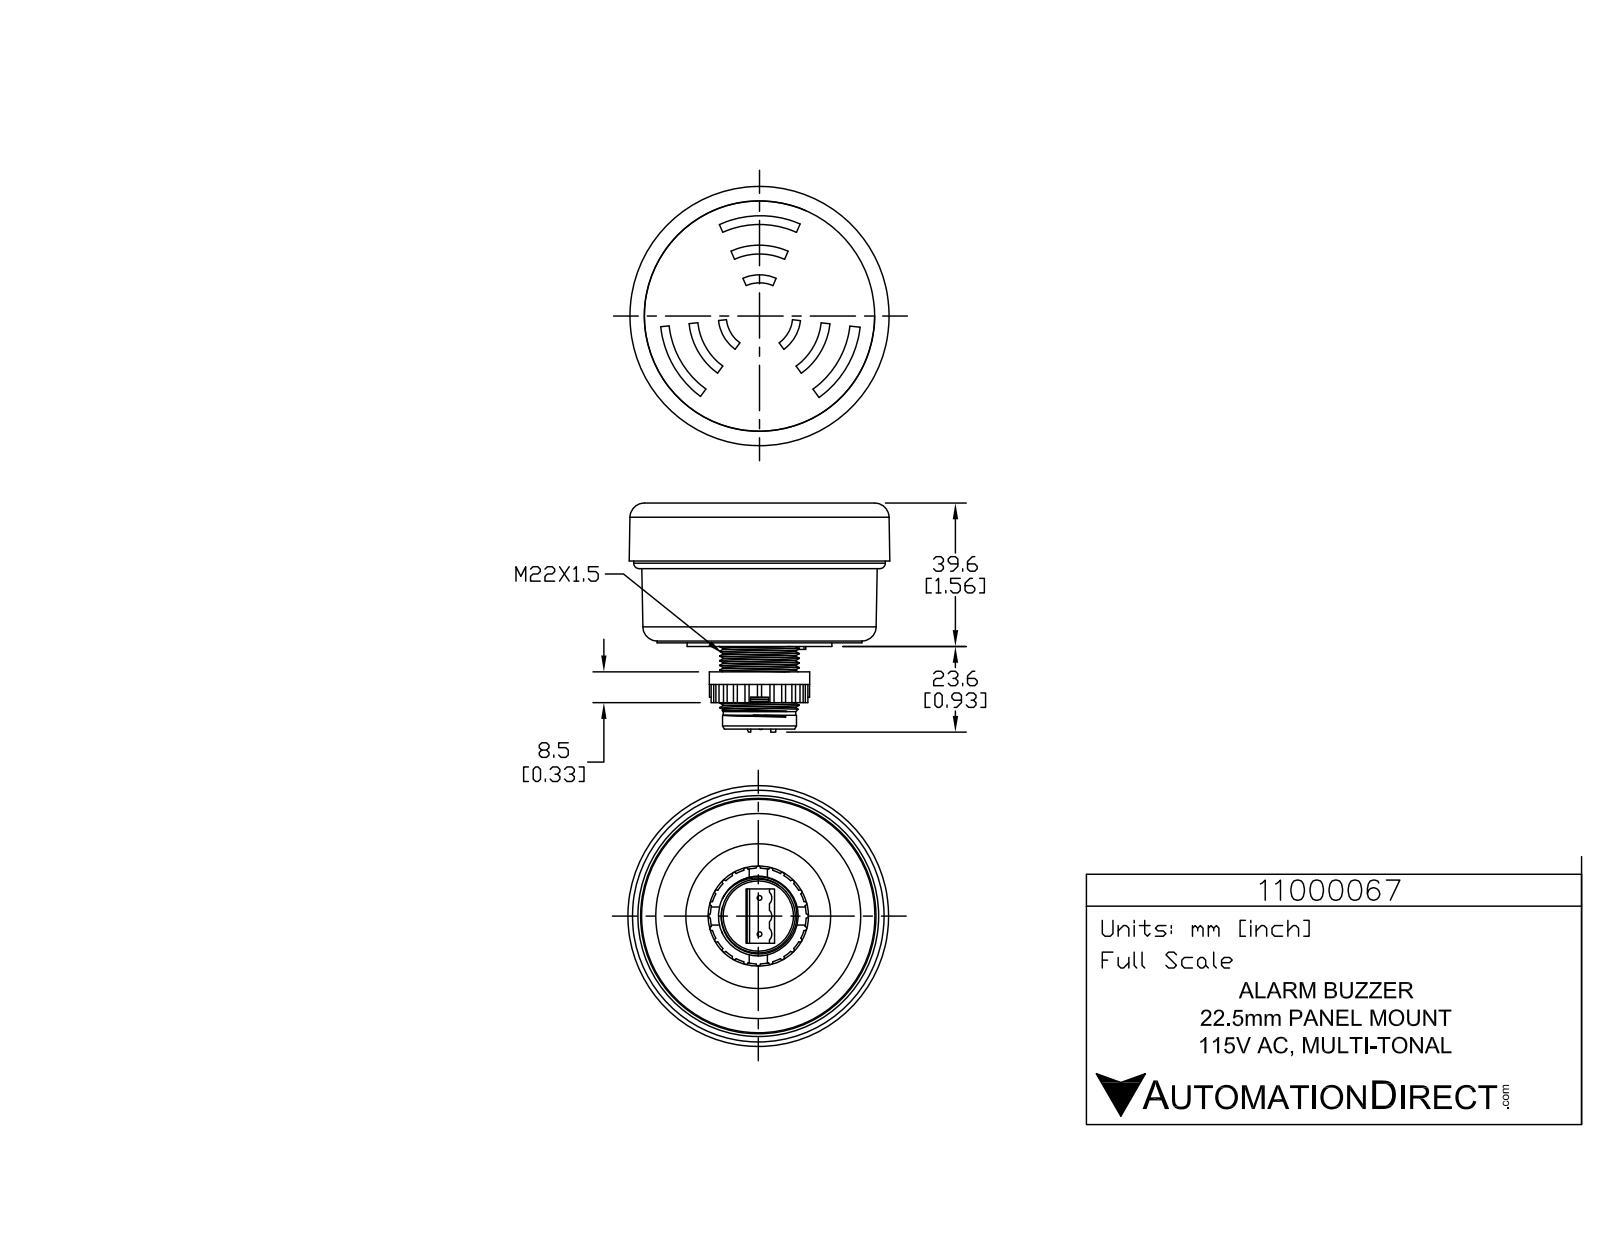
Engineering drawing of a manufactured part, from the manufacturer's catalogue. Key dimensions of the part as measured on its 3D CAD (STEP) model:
Part name (STEP PRODUCT): 11000067
STEP written by: SolidWorks 2017 (AUTOMOTIVE_DESIGN)
Units: inches
Bodies: 1 solid, 1199 faces (768 planar, 326 cylindrical, 105 other)
Overall size (bounding box): 2.839 × 2.837 × 2.49
Volume: 9.029 in³ · Surface area: 31.77 in²
Round holes (diameter × count): ⌀0.049 ×3, ⌀0.106 ×1, ⌀0.424 ×1, ⌀0.906 ×1
Round bosses / shafts (diameter × count): ⌀0.282 ×3, ⌀0.07 ×3, ⌀0.051 ×2, ⌀2.736 ×1, ⌀2.228 ×1, ⌀1.575 ×1, ⌀1.091 ×1, ⌀0.866 ×1
Partial cylindrical surfaces — rounded edges, fillets, slot ends (radius × count): R0.023 ×24, R0.004 ×9, R0.004 ×6, R0.01 ×6, R0.01 ×6, R0.01 ×6, R0.164 ×6, R0.004 ×3
Main face-to-face distances: 1.52, 0.039, 1.559, 0.63, 0.89, 0.929, 0.276, 0.626, 1.555, 1.516
Hole centre spacings: 0.407, 0.613, 0.973
